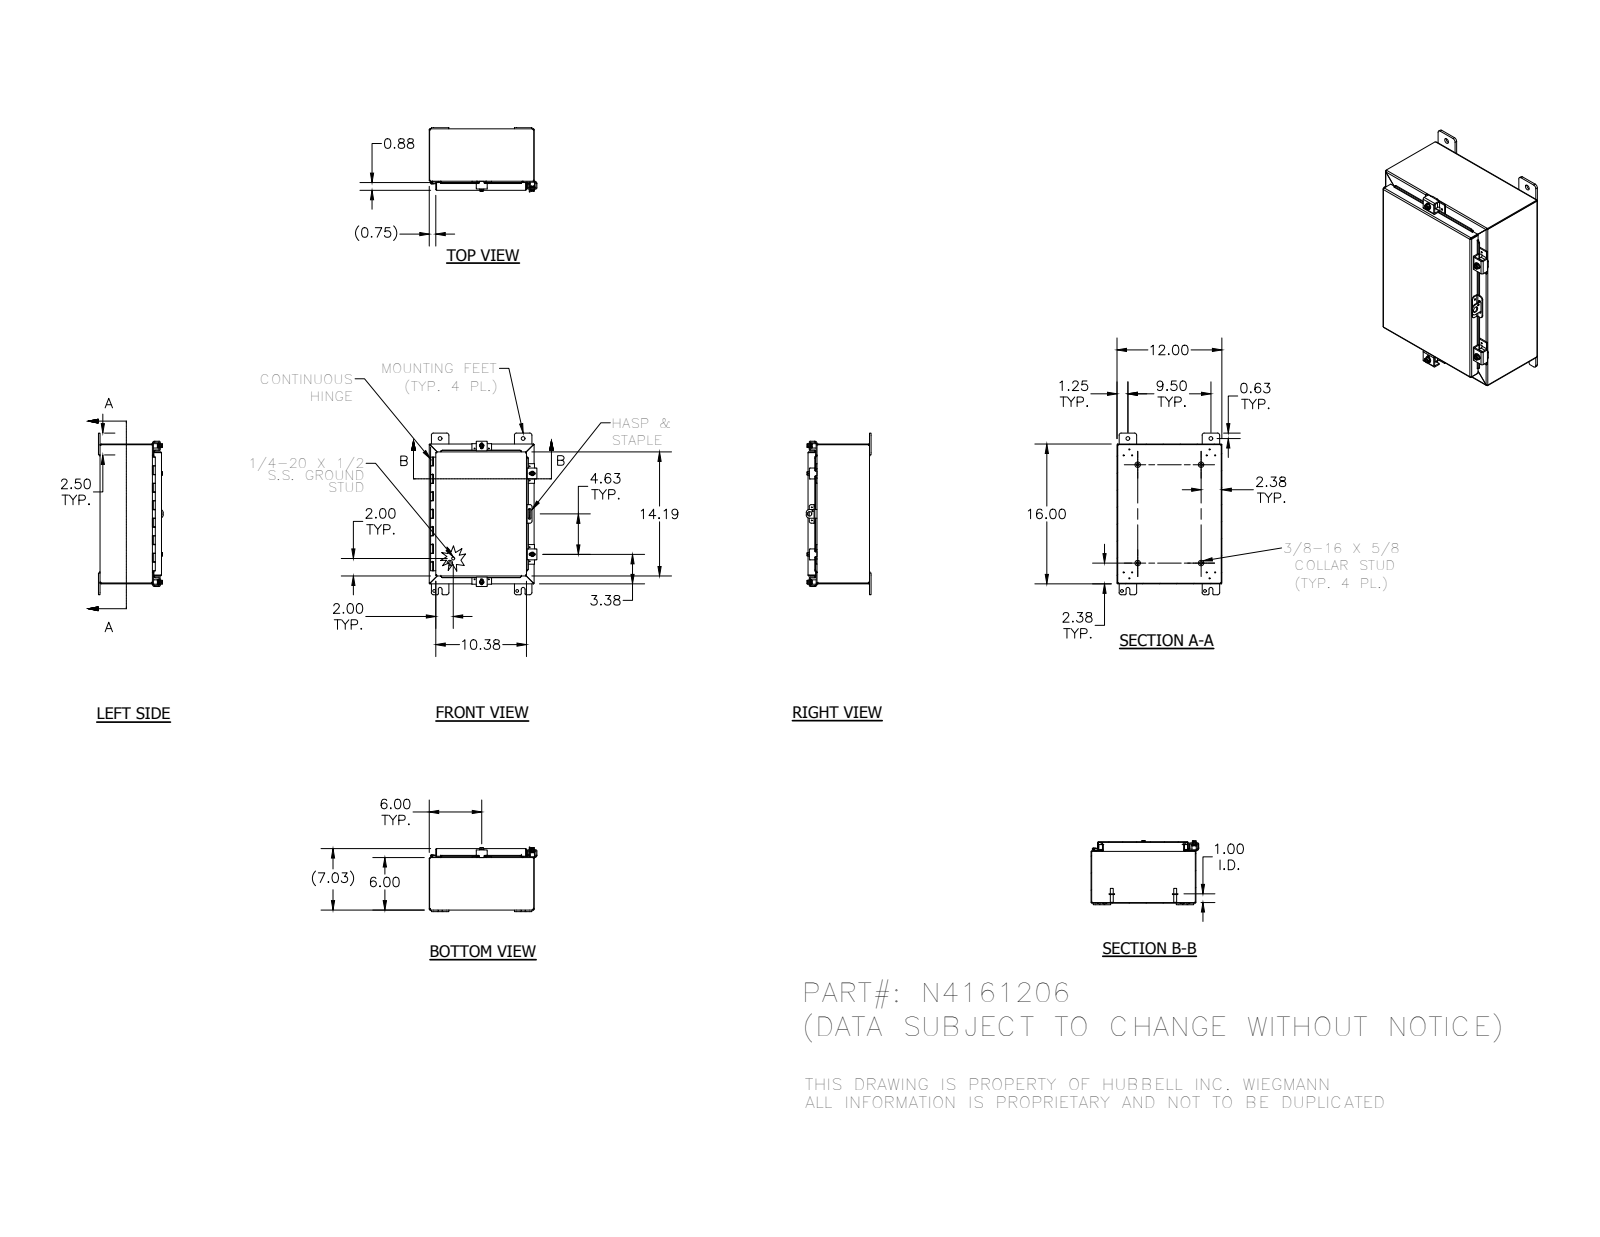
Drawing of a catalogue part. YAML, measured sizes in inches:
part_name: "N4161206BKP_1; HFW30825-2_1; N41612LID_1; N4161206 (+8 more)"
step_written_by: "SolidWorks 2014 (AUTOMOTIVE_DESIGN)"
units: inches
bodies: {solids: 37, faces: 1568, planar: 611, cylindrical: 700, other: 257}
overall_size: [18.5, 12.311, 7.41]
volume: 73.92
surface_area: 1892
round_holes:
  - {diameter: 0.12, count: 12}
  - {diameter: 0.11, count: 11}
  - {diameter: 0.211, count: 4}
  - {diameter: 0.281, count: 4}
  - {diameter: 0.3, count: 4}
  - {diameter: 0.313, count: 4}
  - {diameter: 0.438, count: 4}
  - {diameter: 0.125, count: 1}
  - {diameter: 0.156, count: 1}
  - {diameter: 0.5, count: 1}
round_bosses_or_shafts:
  - {diameter: 0.25, count: 6}
  - {diameter: 0.625, count: 4}
  - {diameter: 0.52, count: 4}
  - {diameter: 0.5, count: 4}
  - {diameter: 0.35, count: 4}
  - {diameter: 0.33, count: 4}
  - {diameter: 0.115, count: 2}
  - {diameter: 0.337, count: 1}
partial_cylinders:
  - {radius: 0.03, count: 49}
  - {radius: 0.125, count: 33}
  - {radius: 0.062, count: 29}
  - {radius: 0.25, count: 29}
  - {radius: 0.031, count: 23}
  - {radius: 0.105, count: 23}
  - {radius: 0.063, count: 10}
  - {radius: 0.07, count: 8}
face_to_face_distances: [0.074, 6.959, 11.926, 6.885, 7.033, 15.926, 5.926, 1.033, 11.852, 12]
hole_center_spacings: [9.5, 0.876, 0.759, 0.94, 0.969, 1.995, 3.543, 3.78]
